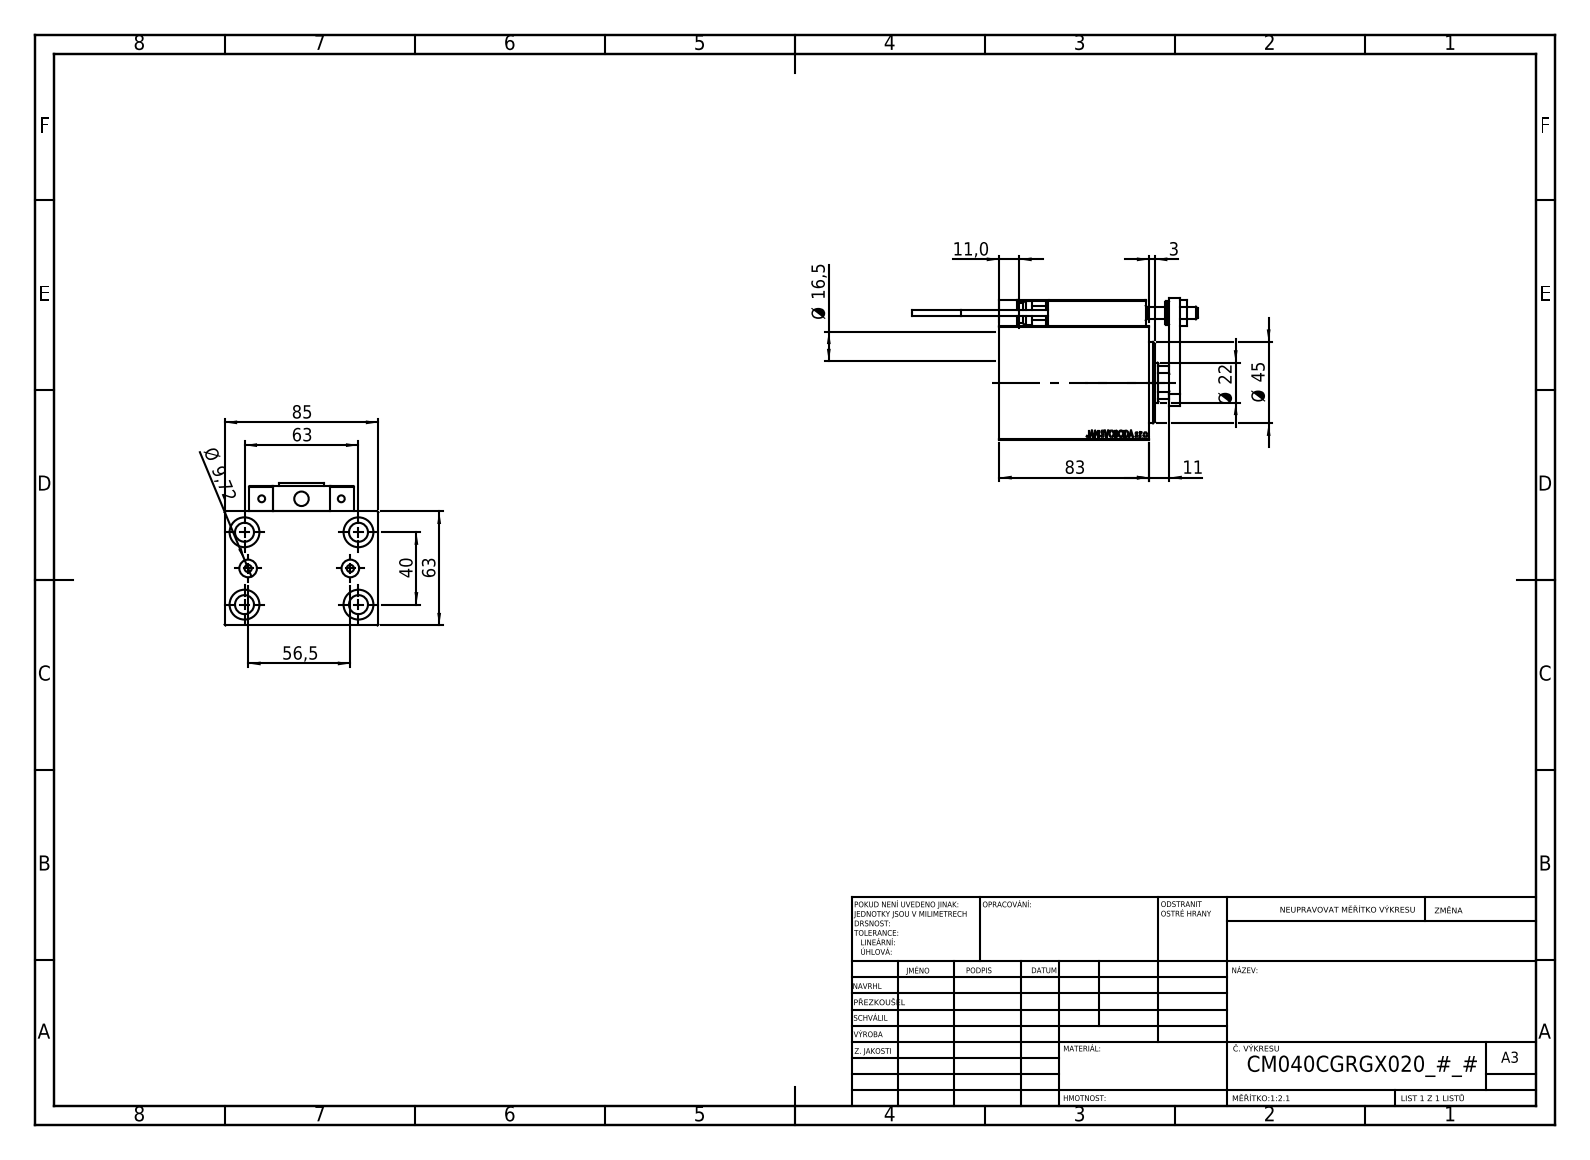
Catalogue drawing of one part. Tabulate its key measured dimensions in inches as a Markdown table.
| quantity | value |
| --- | --- |
| part name | V450CM_C_Body; ALLEN BOLT D5; ALLEN BOLT D8; Block (+8 more) |
| STEP written by | SolidWorks 2019 (CONFIG_CONTROL_DESIGN) |
| units | inches |
| bodies | 23 solids, 1278 faces (560 planar, 184 cylindrical, 534 other) |
| overall size | 6.209 × 3.346 × 3.091 |
| volume | 27.18 in³ |
| surface area | 149.7 in² |
| round holes (diameter × count) | 0.157 × 6, 0.315 × 5, 0.65 × 5, 0.126 × 4, 0.413 × 4, 0.197 × 2, 0.383 × 2, 0.276 × 1, 0.492 × 1, 0.866 × 1, 1.004 × 1, 1.575 × 1 |
| round bosses / shafts (diameter × count) | 0.197 × 2, 0.15 × 2, 0.512 × 1, 0.433 × 1 |
| partial cylindrical surfaces (radius × count) | 0.012 × 30, 0.118 × 2, 0.413 × 1 |
| main face-to-face distances | 2.48, 3.346, 0.551, 3.268, 1.26, 2.008, 0.433, 0.394, 3.031, 2.441 |
| hole center spacings | 1.469, 0.448, 0.787, 0.791, 0.807, 1.165, 1.169, 1.38 |
